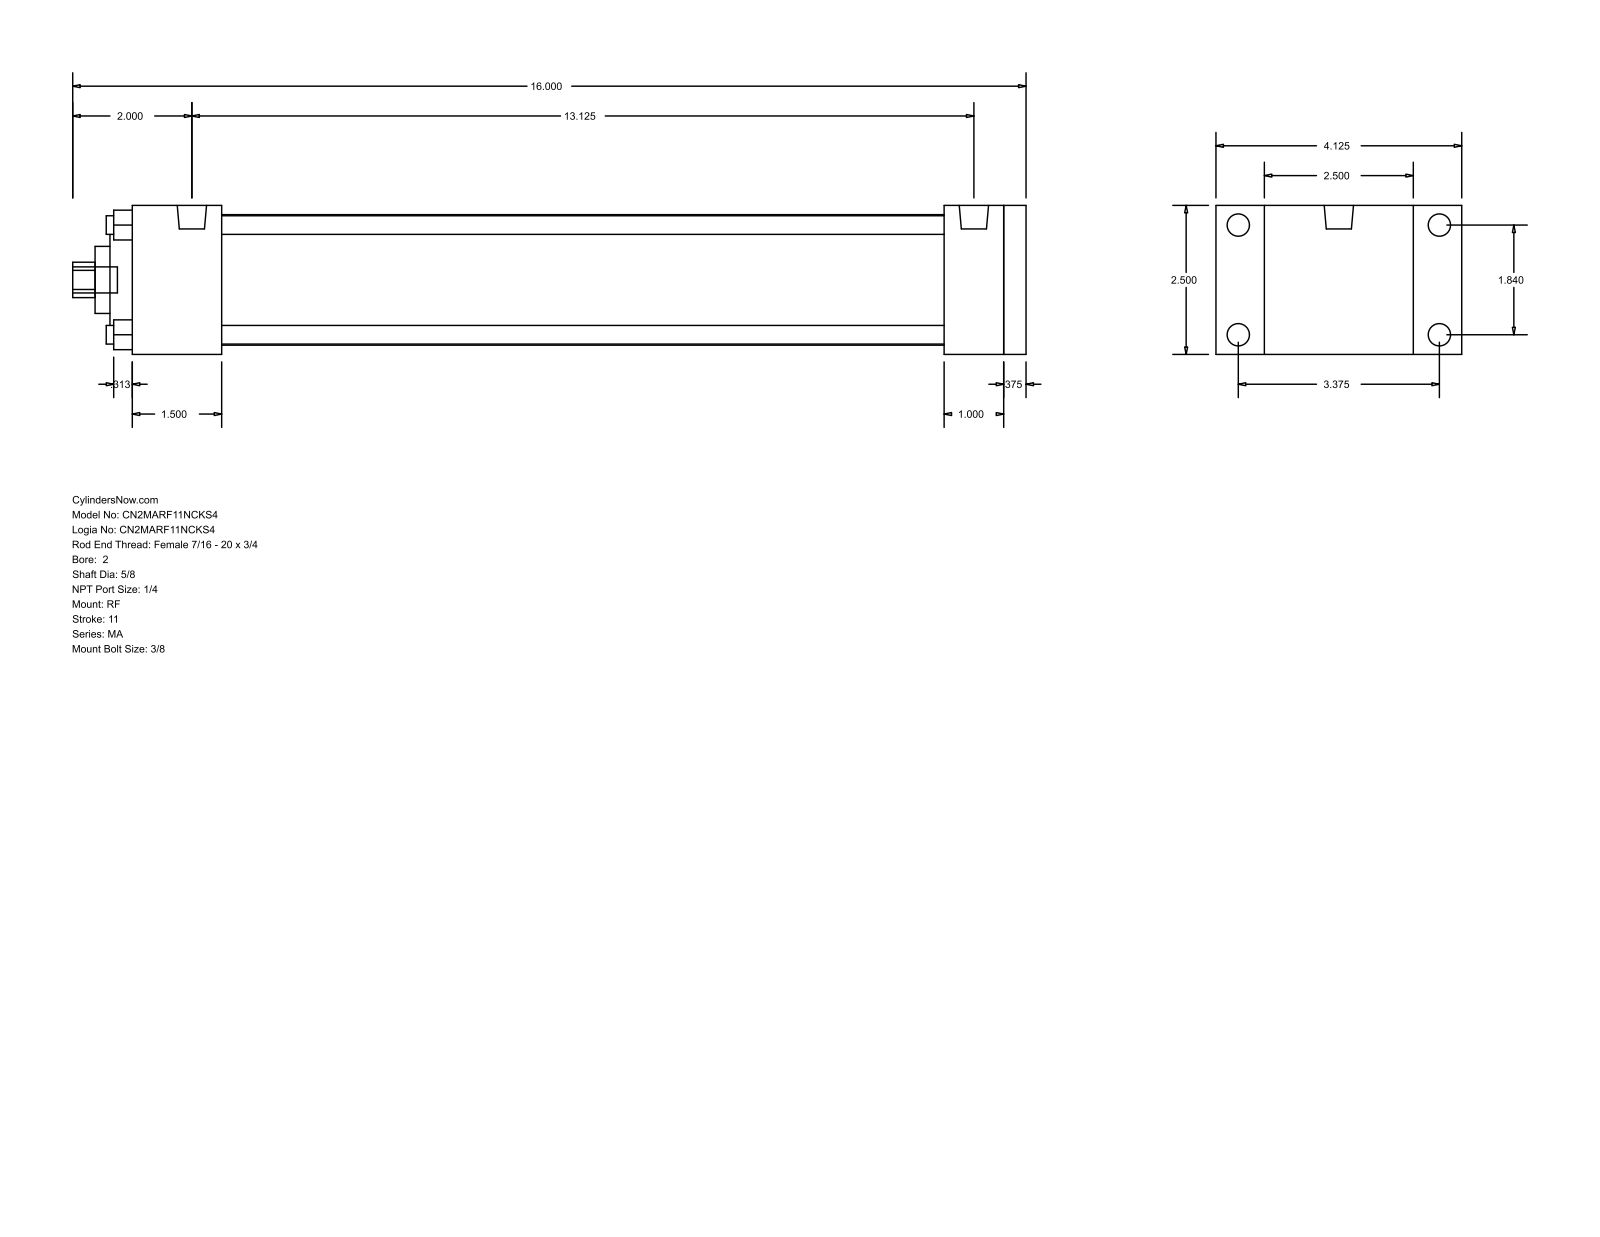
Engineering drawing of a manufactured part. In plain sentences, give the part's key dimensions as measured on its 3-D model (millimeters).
The part is named "MA_RF__0200_0.625". Its 3-D file was written by "GSSL Pune (CONFIG_CONTROL_DESIGN)". It is 0 solids with 94 faces: 65 planar, 29 cylindrical and 0 other. Overall it measures 406.4 by 104.78 by 63.5 millimeters. Round holes: 4 of diameter 7.94, 1 of diameter 15.88, 1 of diameter 28.57, 1 of diameter 50.8, 1 of diameter 55.63. Round bosses or shafts: 4 of diameter 9.53, 4 of diameter 7.94, 2 of diameter 12.49, 1 of diameter 11.11. Partial cylindrical surfaces (rounded edges, fillets, slot ends): 1 of radius 7.54. The main face-to-face distances are 63.5, 9.52, 381, 25.4, 38.1, 371.48, 333.38, 342.9, 346.08, 307.98. The hole center spacings are 33.05, 46.74, 66.1.
